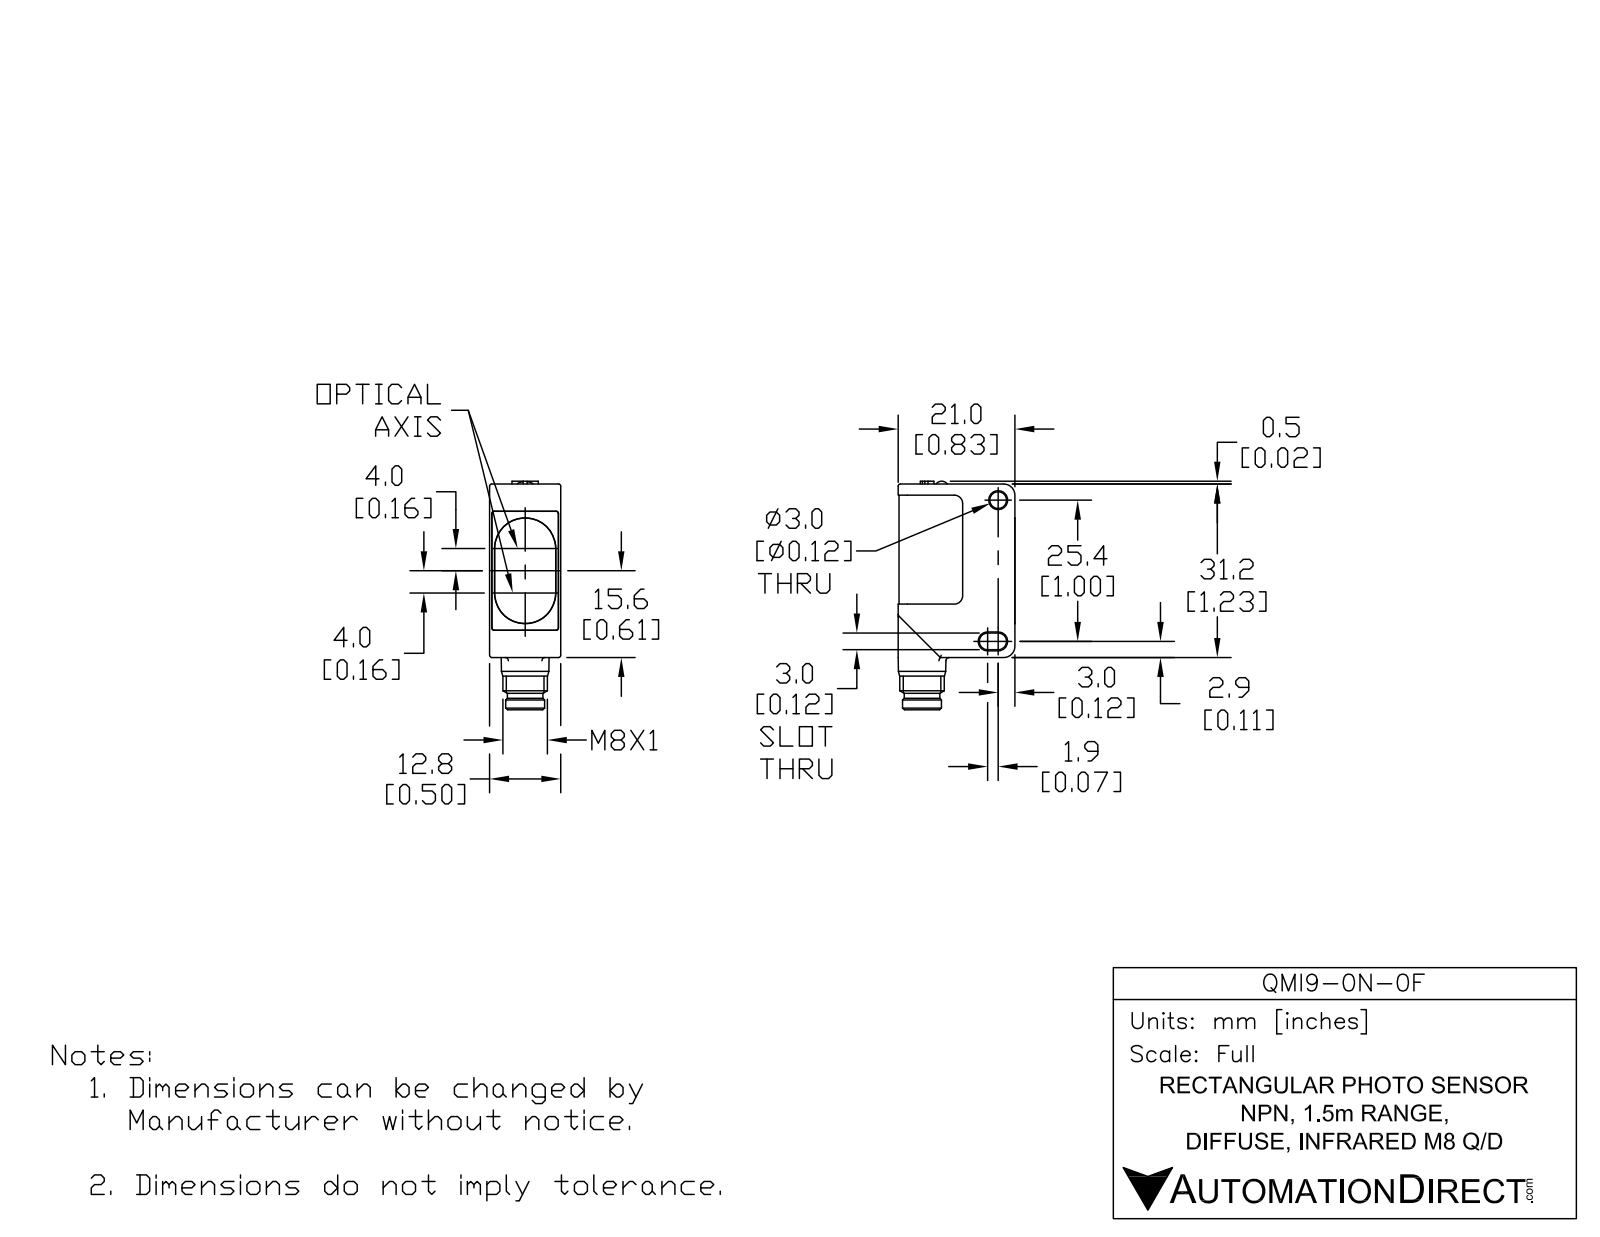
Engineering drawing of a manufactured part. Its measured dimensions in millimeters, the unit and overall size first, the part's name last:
Units: millimetres
Overall size (bounding box): 41.1 × 21 × 12.8
Round holes (diameter × count): ⌀3 ×3, ⌀5.8 ×1
Round bosses / shafts (diameter × count): ⌀1 ×4, ⌀3.5 ×2, ⌀8 ×1, ⌀7 ×1, ⌀6.4 ×1
Partial cylindrical surfaces — rounded edges, fillets, slot ends (radius × count): R0.4 ×10, R0.5 ×9, R1.5 ×6, R0.6 ×4, R1 ×4, R0.2 ×2, R1.1 ×2, R1.7 ×2
Main face-to-face distances: 12.6, 0.5, 12.8, 2.8, 0.4, 12.5, 12.4, 12.2, 1.5, 18.1
Hole centre spacings: 1, 5.2, 6.2
Volume: 7 770 mm³ · Surface area: 4 999 mm²
Bodies: 7 solids, 272 faces (125 planar, 100 cylindrical, 47 other)
Part name (STEP PRODUCT): QMI9-0N-0F
STEP written by: SolidWorks 2017 (AUTOMOTIVE_DESIGN)
